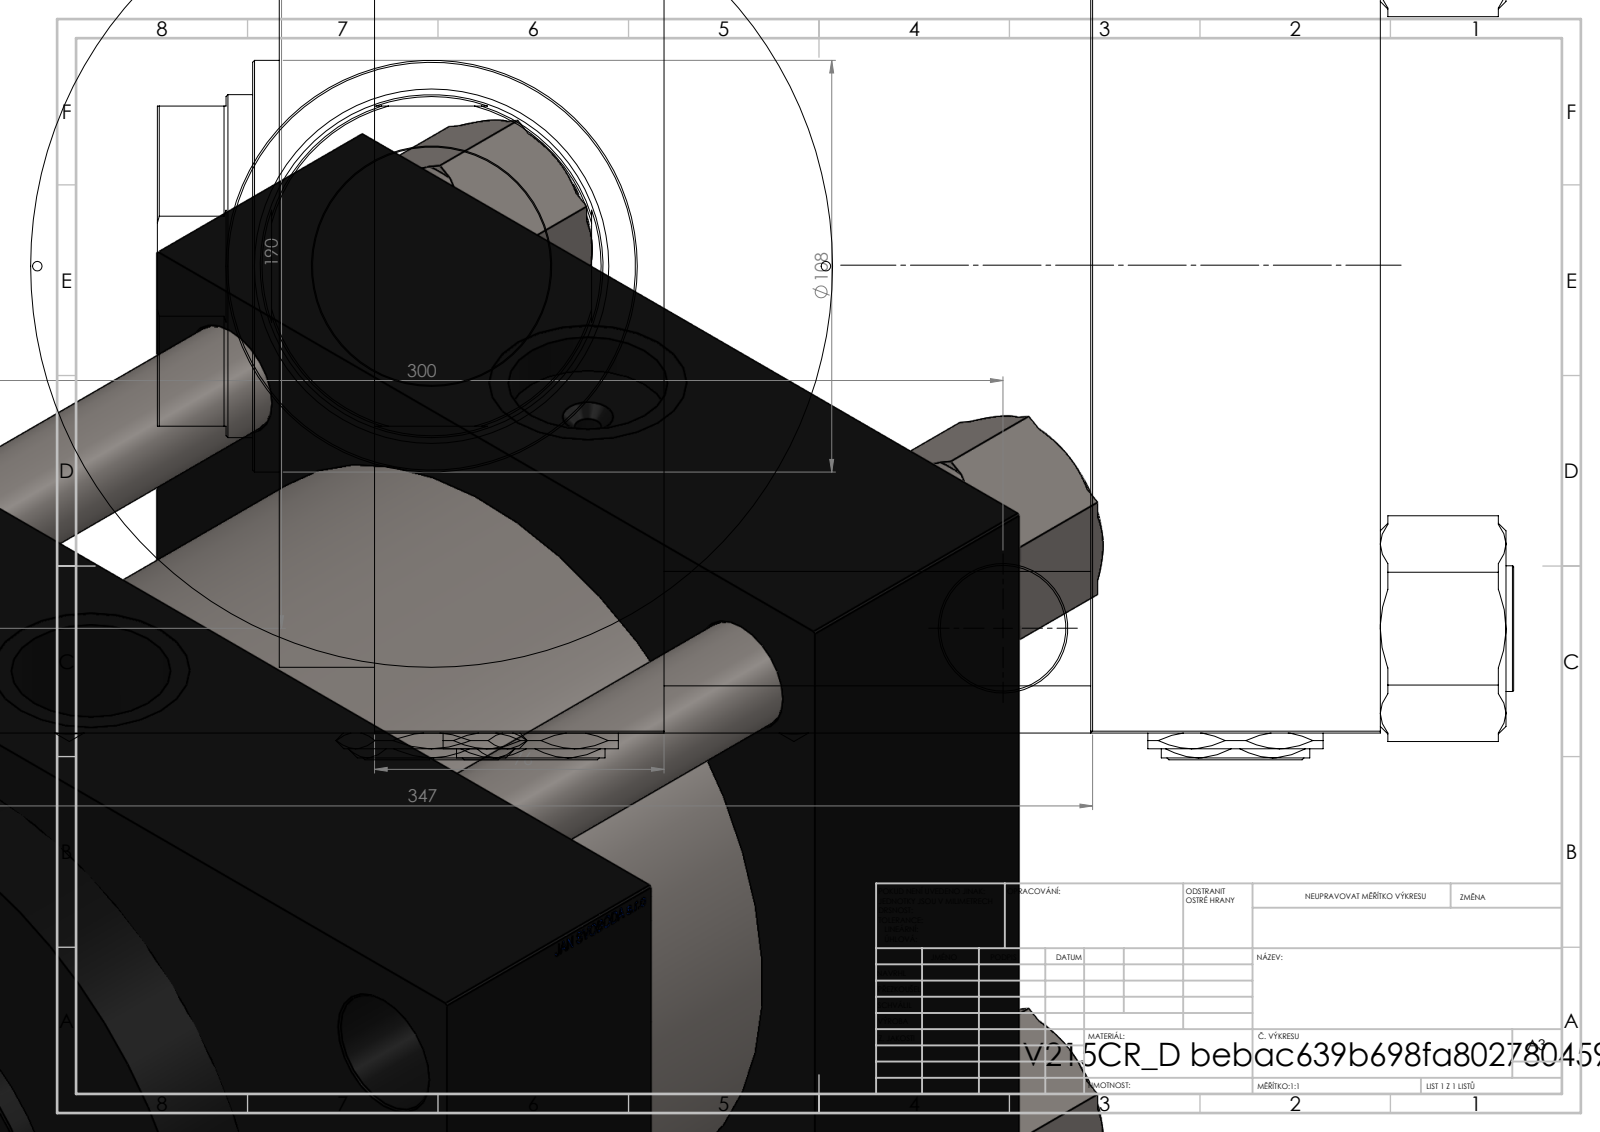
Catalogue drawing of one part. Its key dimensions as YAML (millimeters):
part_name: "V215CR_D_Body; V215_VC_A; V215CR_VCP_D; NUT_M5_D (+2 more)"
step_written_by: "SolidWorks 2019 (CONFIG_CONTROL_DESIGN)"
units: millimeters
bodies: {solids: 13, faces: 1255, planar: 593, cylindrical: 102, other: 560}
overall_size: [356, 347, 254.22]
volume: 14650000
surface_area: 1107000
round_holes:
  - {diameter: 30, count: 4}
  - {diameter: 33, count: 4}
  - {diameter: 2.5, count: 2}
  - {diameter: 7, count: 2}
  - {diameter: 41.92, count: 2}
  - {diameter: 52, count: 2}
  - {diameter: 62.5, count: 1}
  - {diameter: 90, count: 1}
  - {diameter: 93, count: 1}
  - {diameter: 146, count: 1}
  - {diameter: 200, count: 1}
  - {diameter: 210.5, count: 1}
round_bosses_or_shafts:
  - {diameter: 33, count: 4}
  - {diameter: 206, count: 1}
  - {diameter: 108, count: 1}
partial_cylinders:
  - {radius: 44, count: 1}
face_to_face_distances: [76, 188, 245, 112, 264, 245.74, 169.74, 57.74, 18.26, 296]
hole_center_spacings: [54.9, 95.47, 105.77, 134.49, 177.55, 190.2, 197.87, 220.2]
